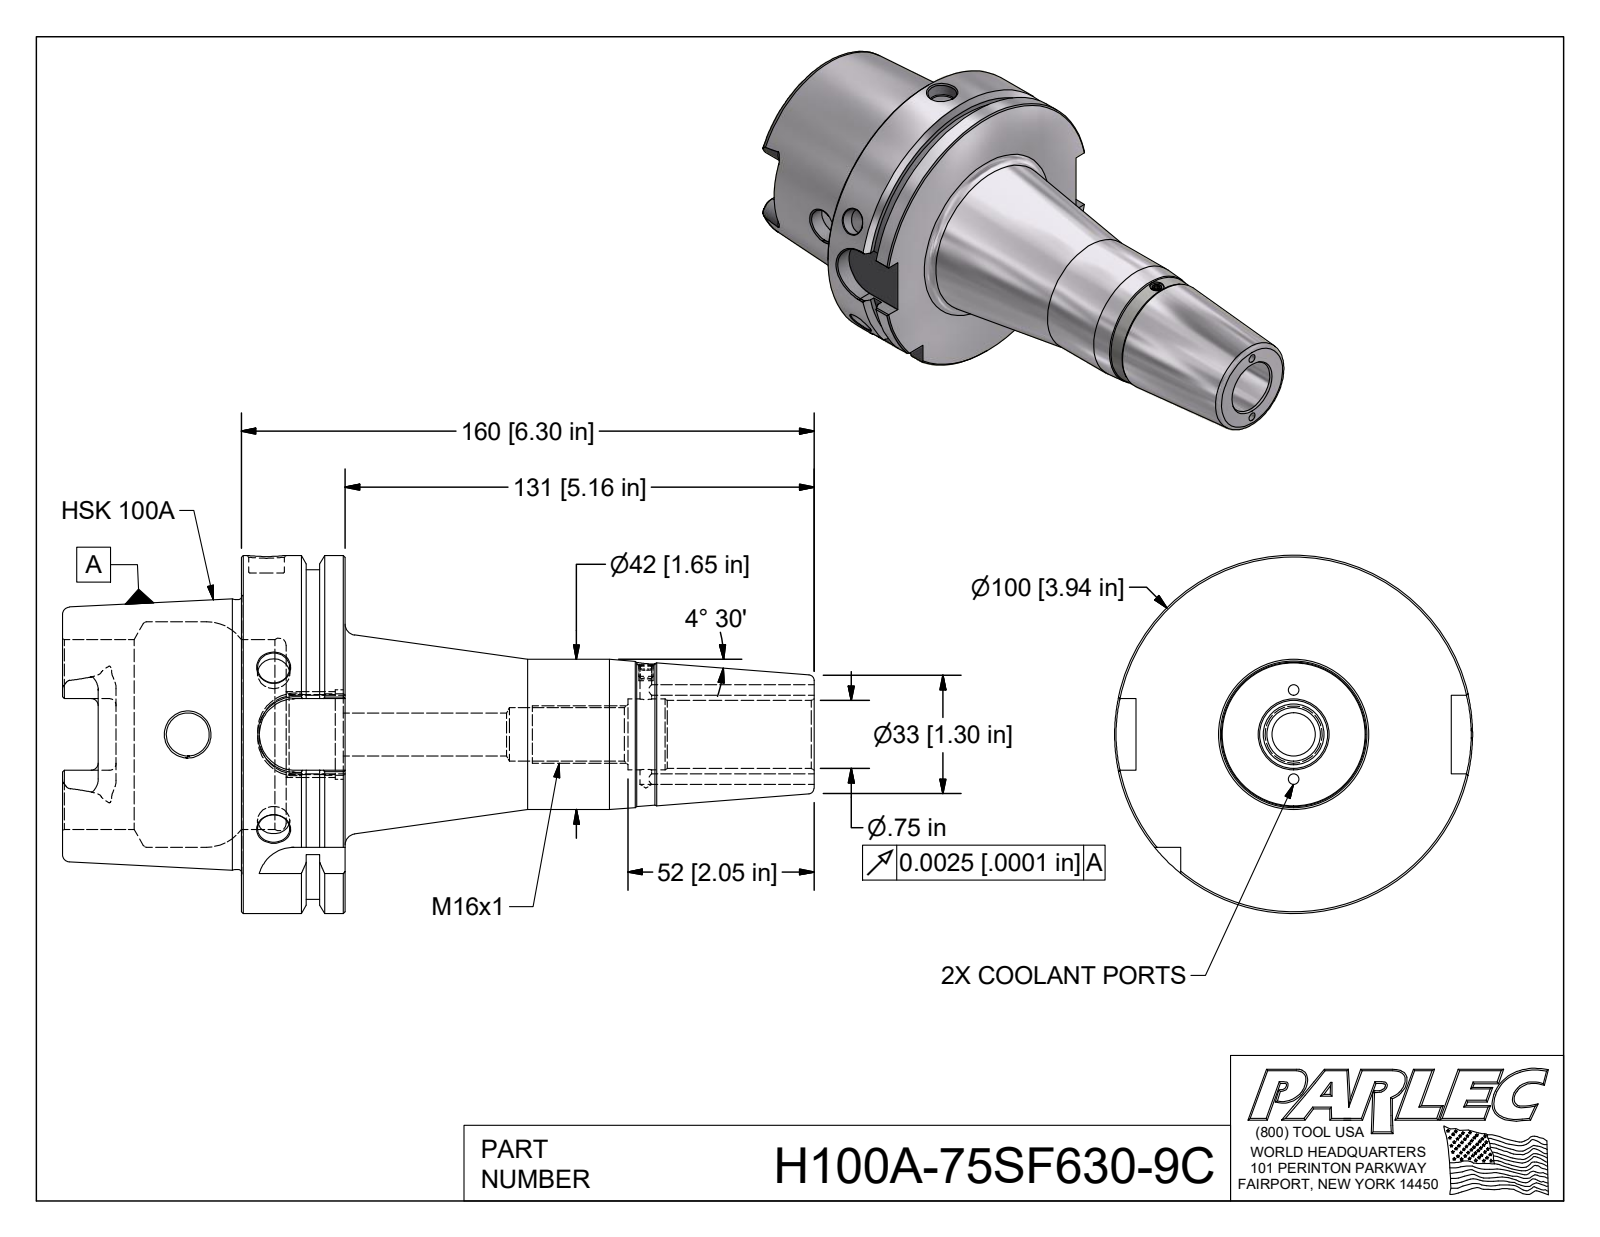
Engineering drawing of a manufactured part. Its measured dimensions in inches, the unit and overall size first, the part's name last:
Units: inches
Overall size (bounding box): 8.268 × 3.937 × 3.937
Round holes (diameter × count): ⌀0.118 ×2, ⌀0.354 ×2, ⌀0.472 ×2, ⌀0.128 ×1, ⌀0.197 ×1, ⌀0.394 ×1, ⌀0.587 ×1, ⌀0.749 ×1, ⌀0.779 ×1, ⌀0.881 ×1, ⌀0.985 ×1, ⌀2.087 ×1
Round bosses / shafts (diameter × count): ⌀3.937 ×1, ⌀3.622 ×1, ⌀2.967 ×1, ⌀1.654 ×1
Partial cylindrical surfaces — rounded edges, fillets, slot ends (radius × count): R0.079 ×6, R0.192 ×4, R0.394 ×4
Main face-to-face distances: 1.142, 0.492, 0.65, 3.11, 1.969, 2.461, 3.465, 2.83, 0.861, 0.369
Hole centre spacings: 0.49, 0.98, 4.174
Volume: 25.61 in³ · Surface area: 113.3 in²
Bodies: 1 solid, 154 faces (49 planar, 42 cylindrical, 63 other)
STEP written by: Autodesk Inventor 2018 (AUTOMOTIVE_DESIGN)
